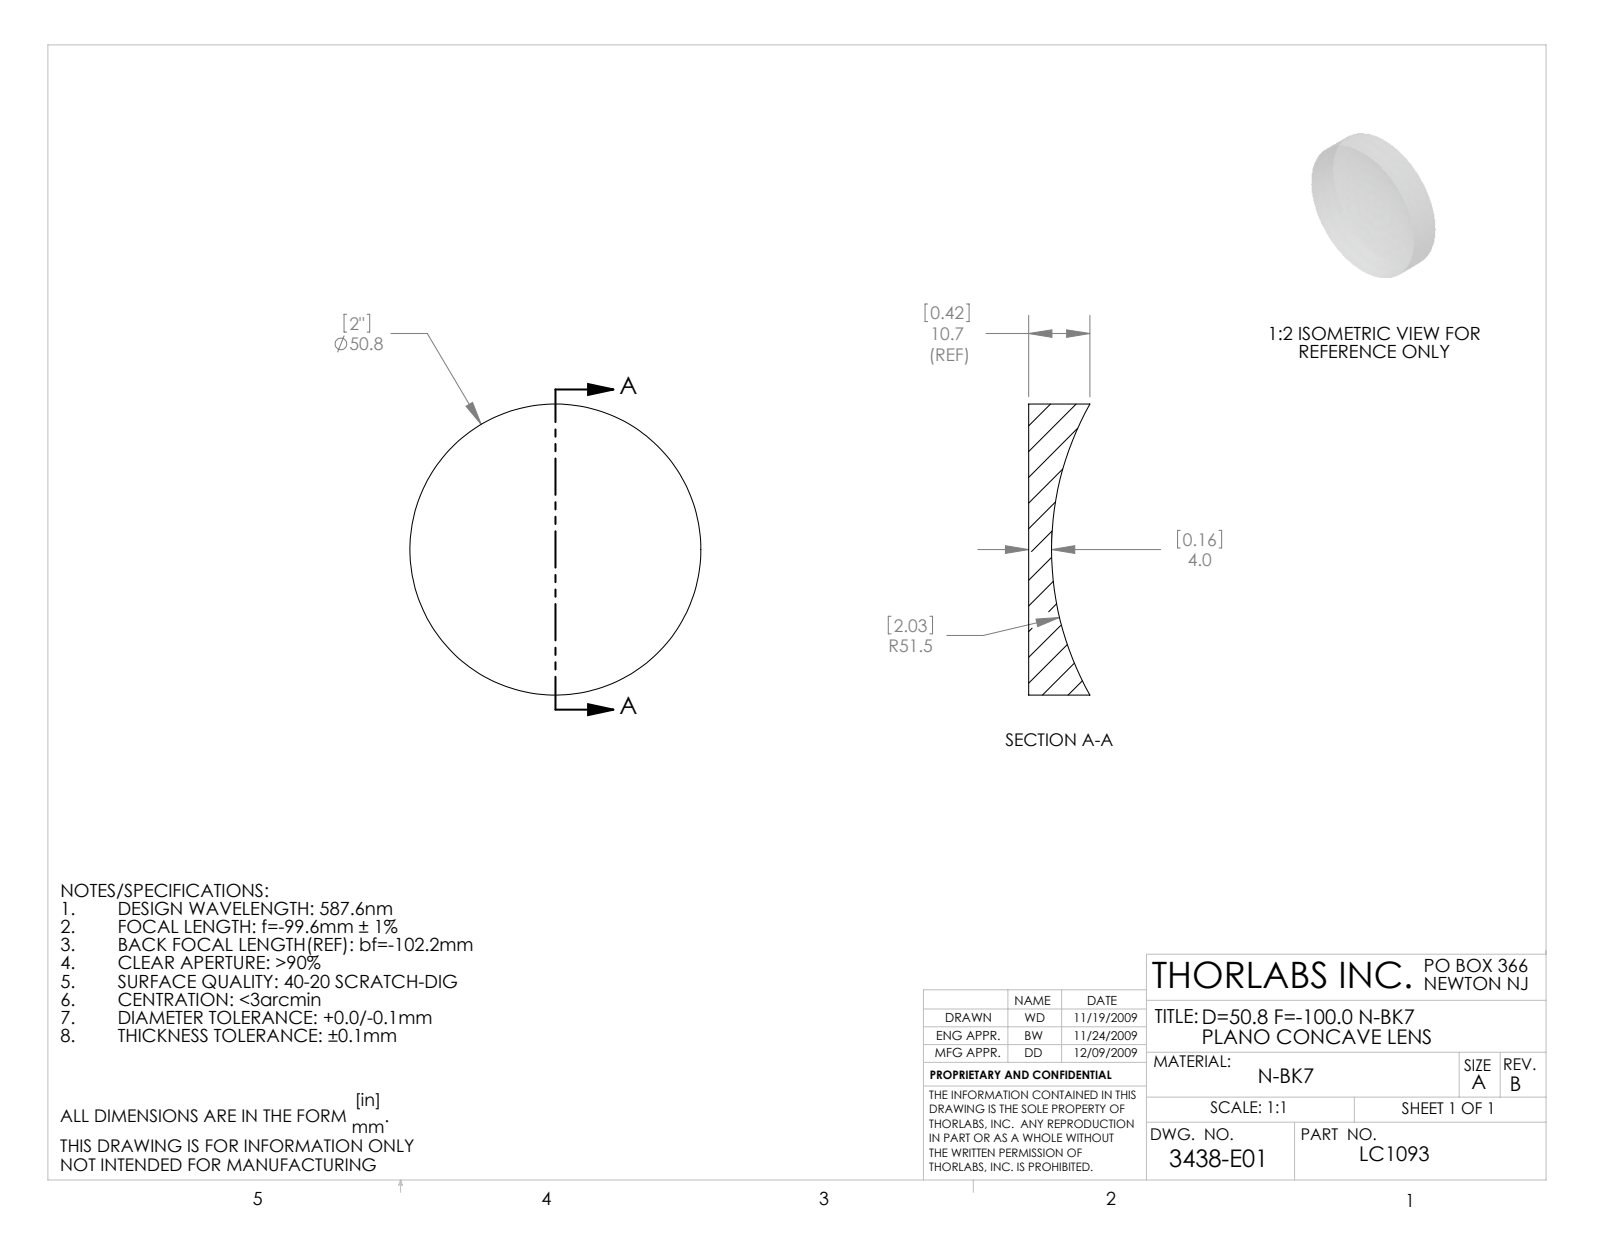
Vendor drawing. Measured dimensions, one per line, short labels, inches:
name: 3438-E0W
written by: SolidWorks 2009 (AUTOMOTIVE_DESIGN)
unit: in
bodies: 1 solid, 5 faces (1 planar, 2 cylindrical, 2 other)
size: 2 × 2 × 0.422
volume: 0.9 in³; area: 9.15 in²
bosses: 1× ⌀2
